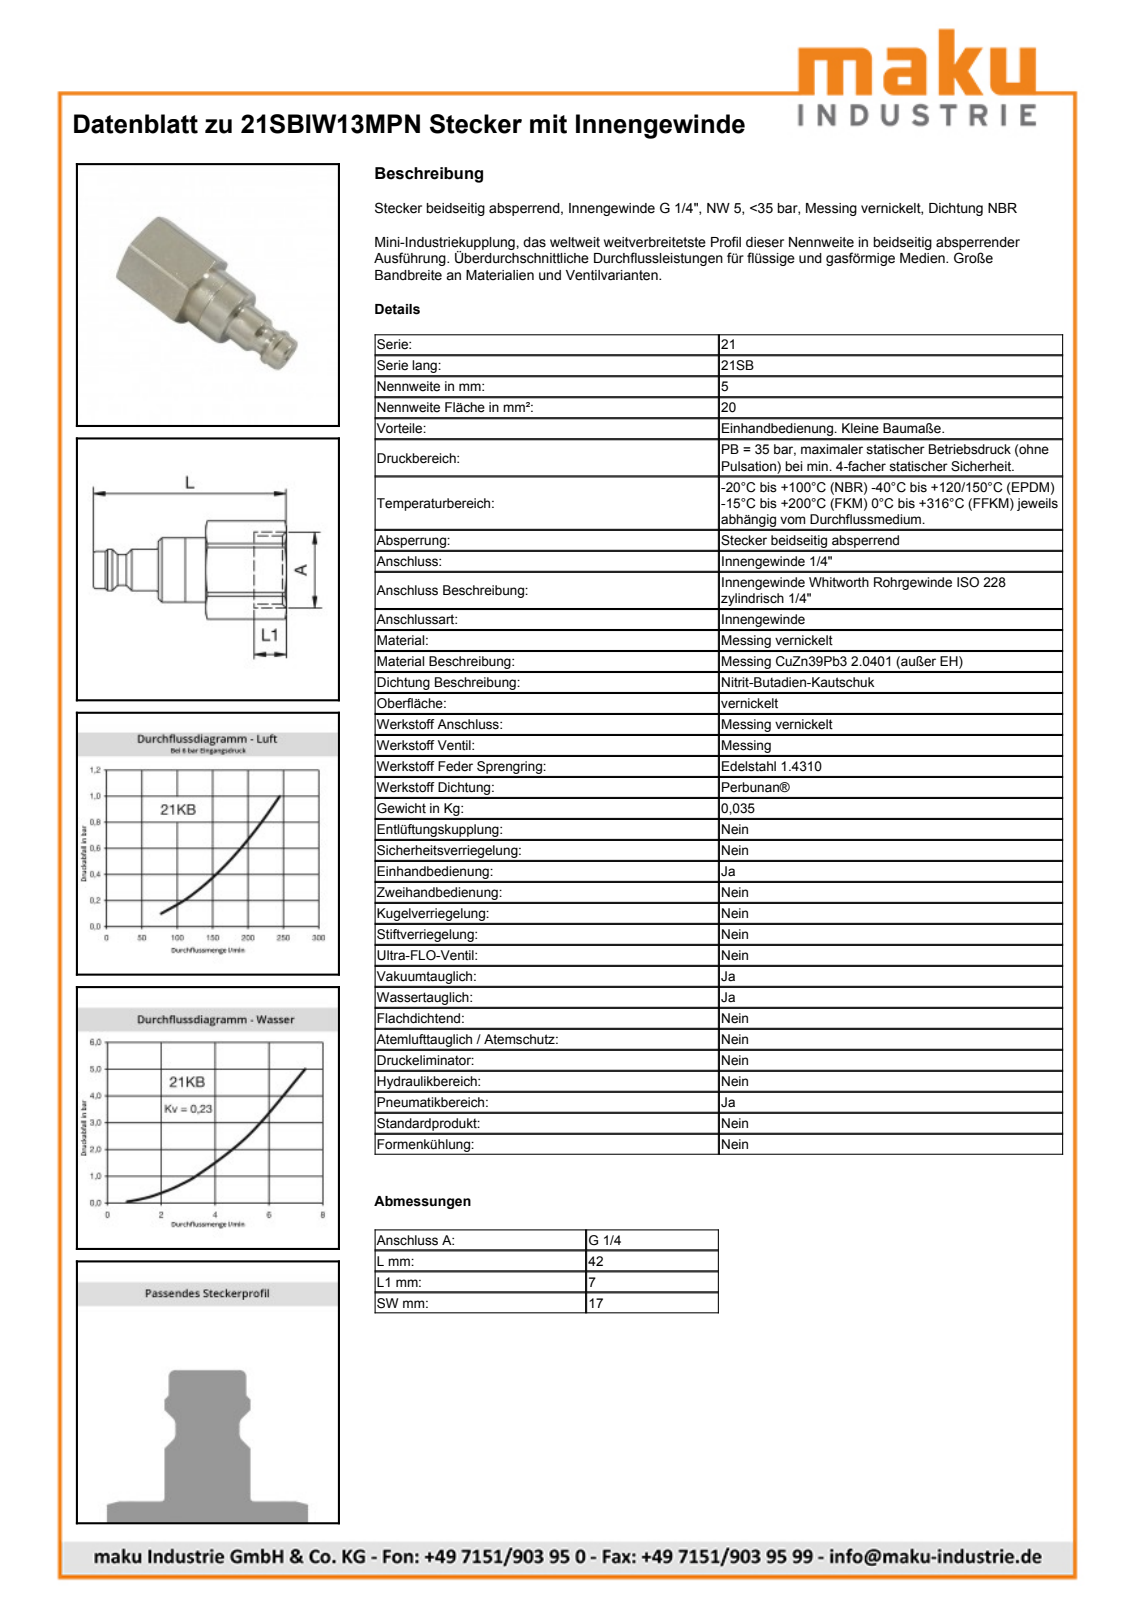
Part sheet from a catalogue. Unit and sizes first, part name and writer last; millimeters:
Units: millimetres
Overall size (bounding box): 42 × 18.86 × 18.5
Round holes (diameter × count): ⌀7.5 ×1, ⌀11.45 ×1
Round bosses / shafts (diameter × count): ⌀14 ×1, ⌀11.74 ×1, ⌀9 ×1, ⌀8.1 ×1, ⌀6.65 ×1
Partial cylindrical surfaces — rounded edges, fillets, slot ends (radius × count): R9.57 ×1
Main face-to-face distances: 17, 16.98, 9, 8.55, 17.55, 10.35, 18.9, 27.9, 14.1, 24.45
Volume: 5 789 mm³ · Surface area: 2 632 mm²
Bodies: 1 solid, 49 faces (12 planar, 14 cylindrical, 23 other)
Part name (STEP PRODUCT): D107129
STEP written by: Autodesk Inventor 2013 (AUTOMOTIVE_DESIGN)
